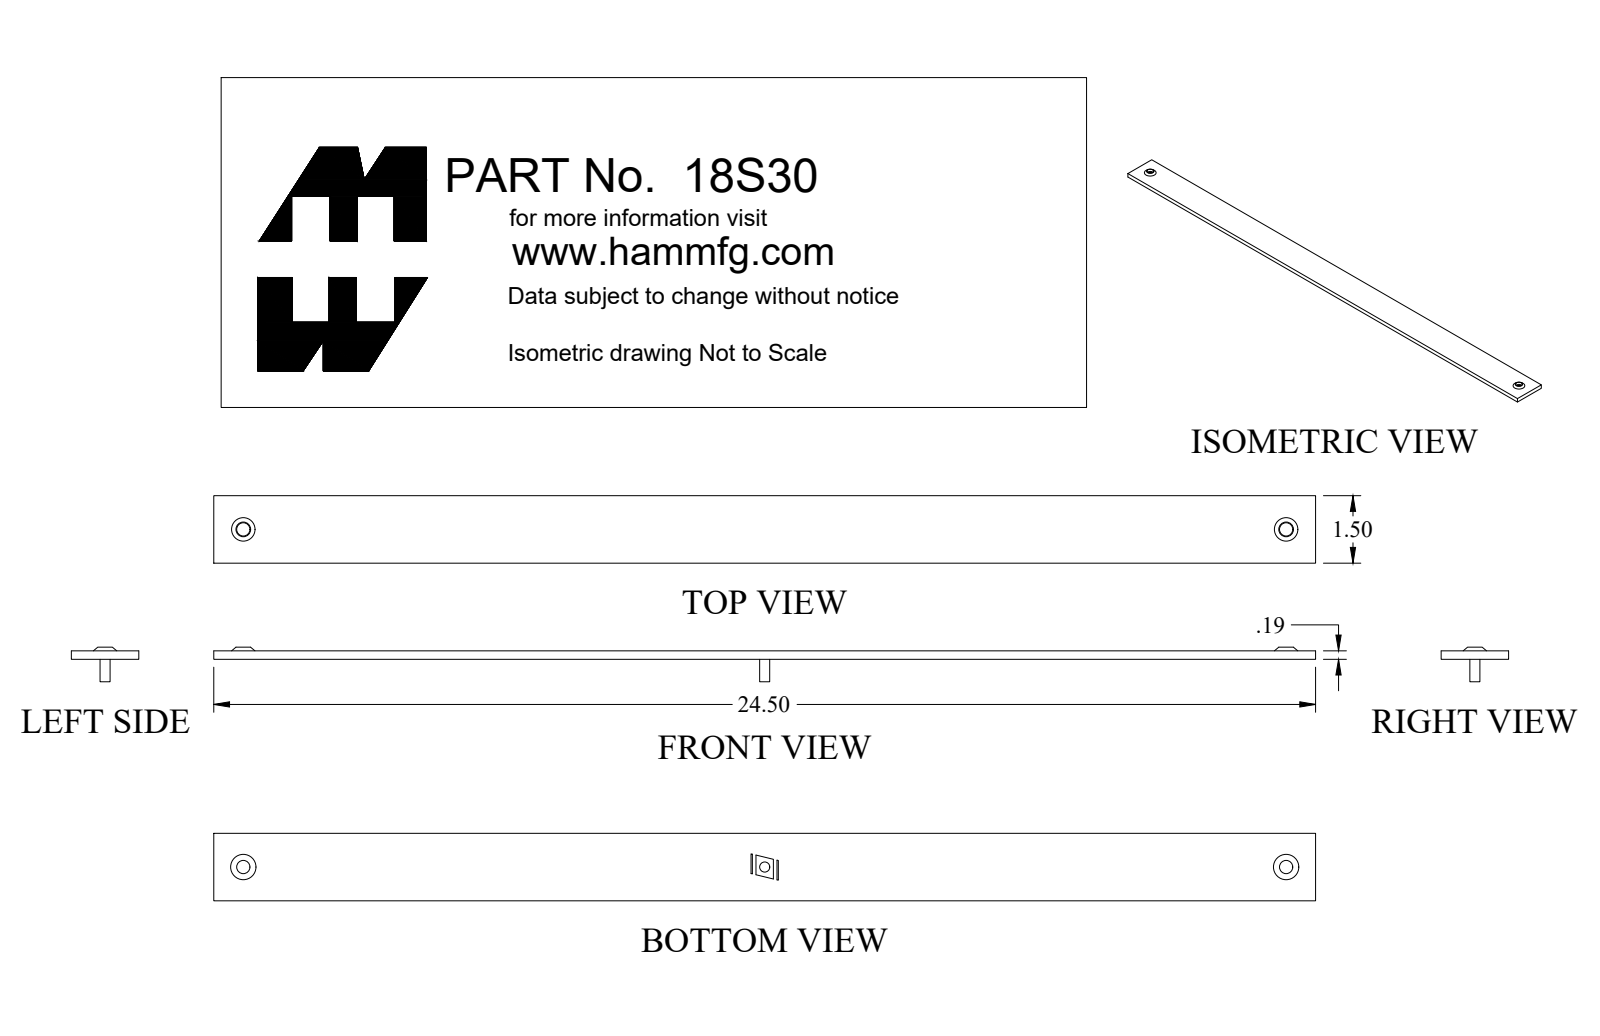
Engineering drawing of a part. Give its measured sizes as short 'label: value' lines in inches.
name: 18S30_Default
written by: SolidWorks 2018 (CONFIG_CONTROL_DESIGN)
unit: in
bodies: 1 solid, 20 faces (8 planar, 4 cylindrical, 8 other)
size: 24.5 × 1.5 × 0.27
volume: 6.871 in³; area: 83.49 in²
holes: 2× ⌀0.296
face distances: 0.188, 1.5, 24.5, 0.27, 0.082
hole spacings: 23.188
